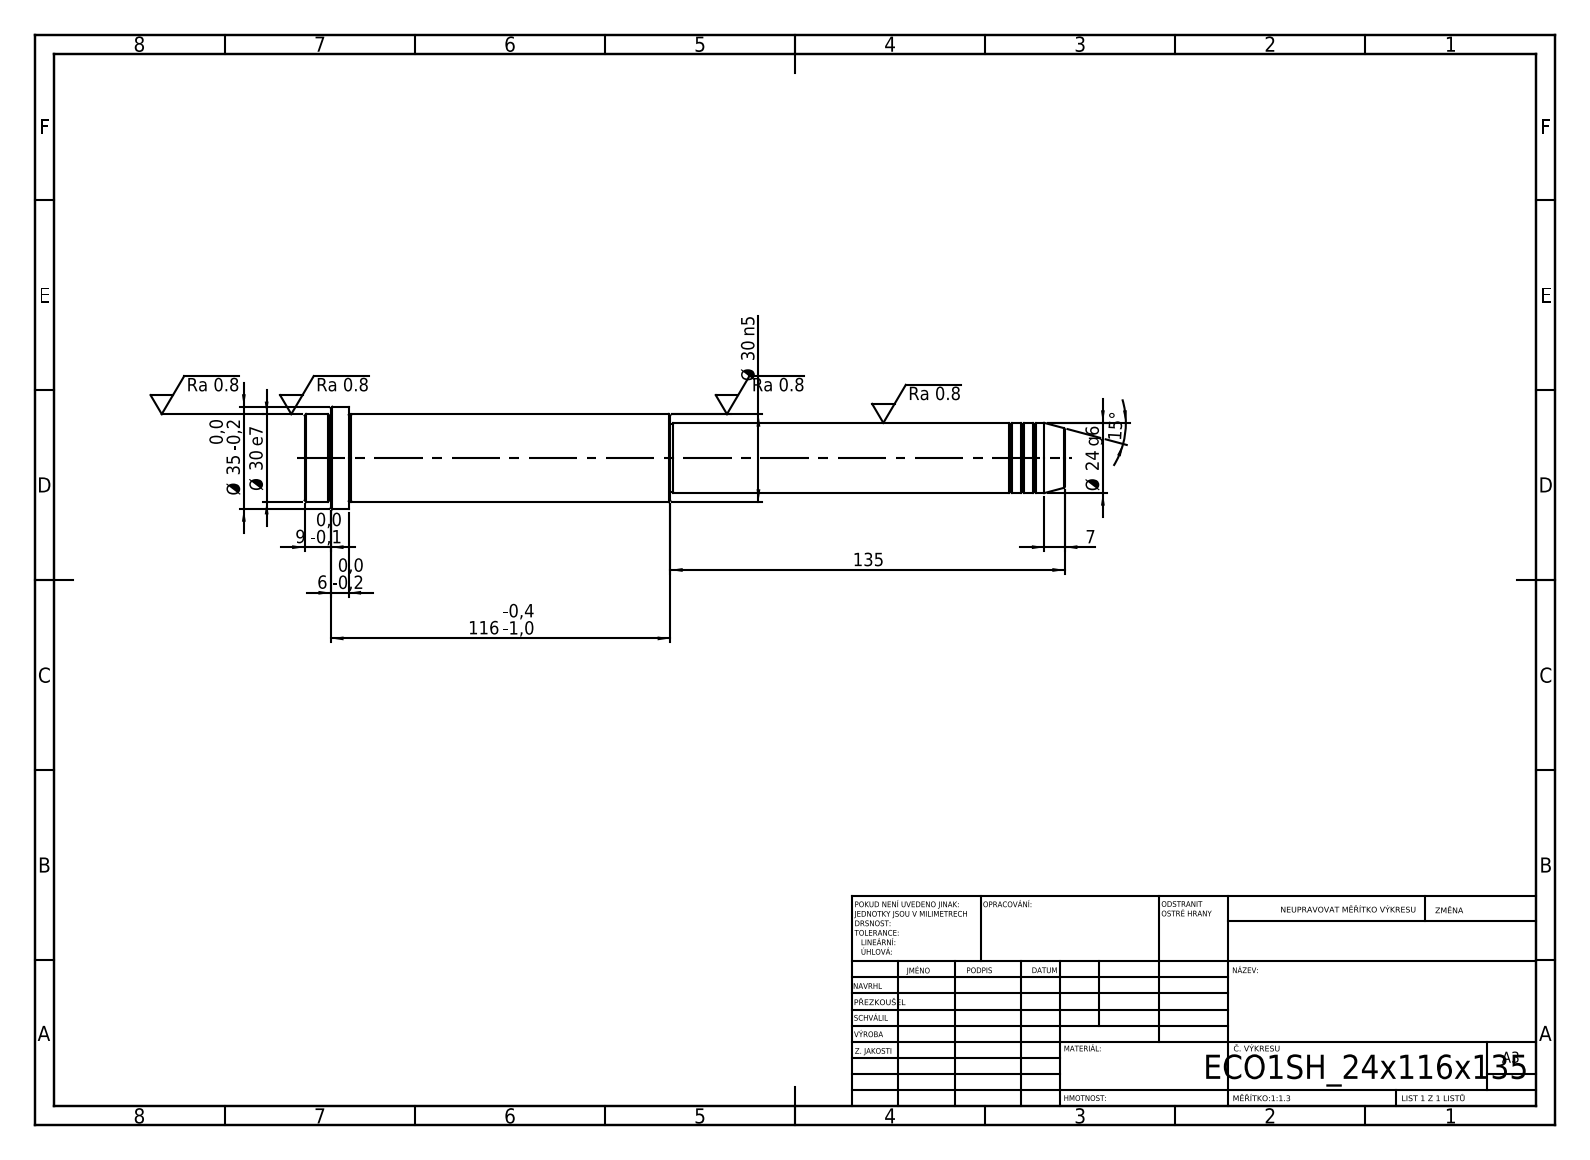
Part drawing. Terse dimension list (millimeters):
written by: SolidWorks 2019 (CONFIG_CONTROL_DESIGN)
unit: mm
bodies: 1 solid, 52 faces (6 planar, 16 cylindrical, 30 other)
size: 260 × 35 × 35
volume: 150 256 mm³; area: 24 020 mm²
bosses: 1× ⌀35, 1× ⌀30, 1× ⌀24, 1× ⌀23
face distances: 260, 245, 15, 135, 110, 125, 251, 116, 6, 9
